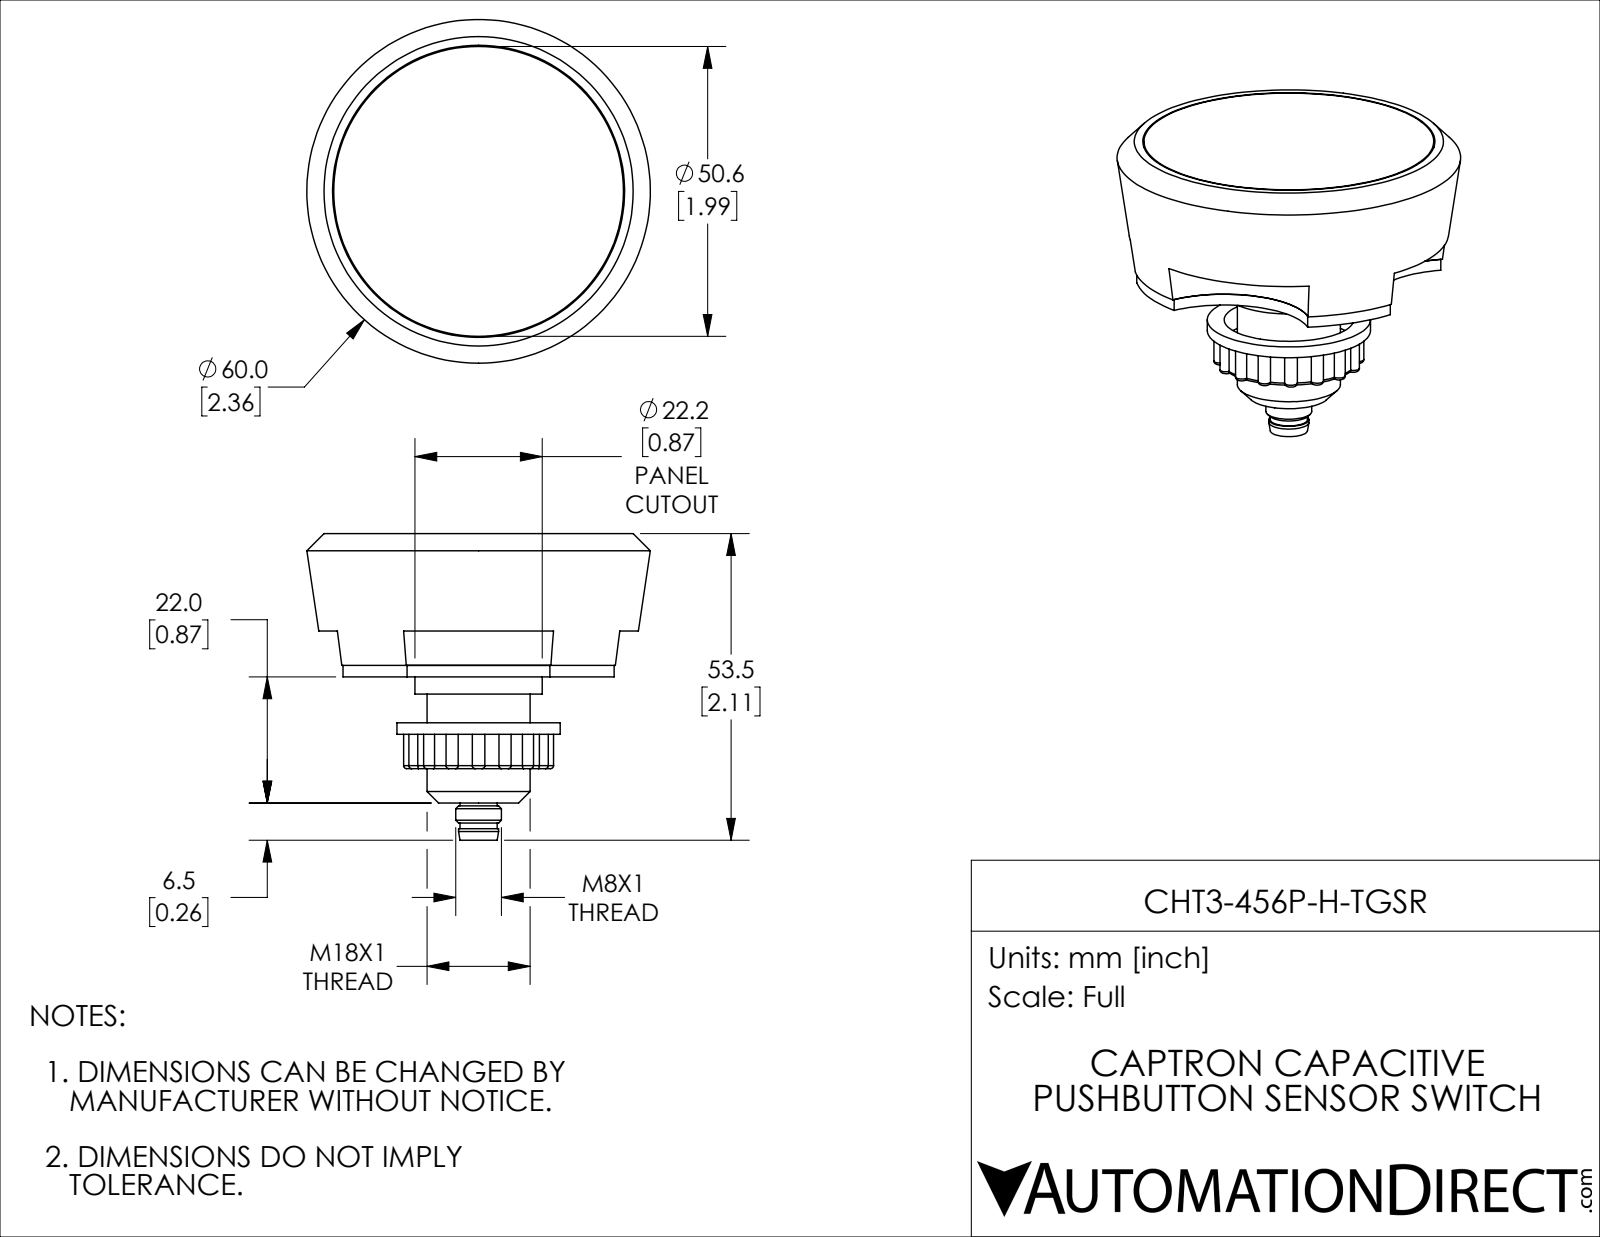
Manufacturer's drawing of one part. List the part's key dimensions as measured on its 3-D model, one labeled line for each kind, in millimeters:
Part name (STEP PRODUCT): CHT3-456P-H-TGSR
STEP written by: SolidWorks 2019 (CONFIG_CONTROL_DESIGN)
Units: millimetres
Bodies: 9 solids, 197 faces (27 planar, 95 cylindrical, 75 other)
Overall size (bounding box): 60 × 60 × 53.5
Volume: 63 958 mm³ · Surface area: 20 586 mm²
Round holes (diameter × count): ⌀6 ×1, ⌀17 ×1, ⌀22.6 ×1, ⌀51 ×1
Round bosses / shafts (diameter × count): ⌀1 ×4, ⌀50.6 ×1, ⌀28.5 ×1, ⌀22.2 ×1, ⌀18 ×1, ⌀8 ×1, ⌀7 ×1, ⌀6.5 ×1
Partial cylindrical surfaces — rounded edges, fillets, slot ends (radius × count): R1.1 ×16, R15 ×4, R12 ×1, R26.75 ×1
Main face-to-face distances: 23, 20.2, 2.8, 0.5, 20.7, 2.3, 2, 8, 22.2, 22.7
